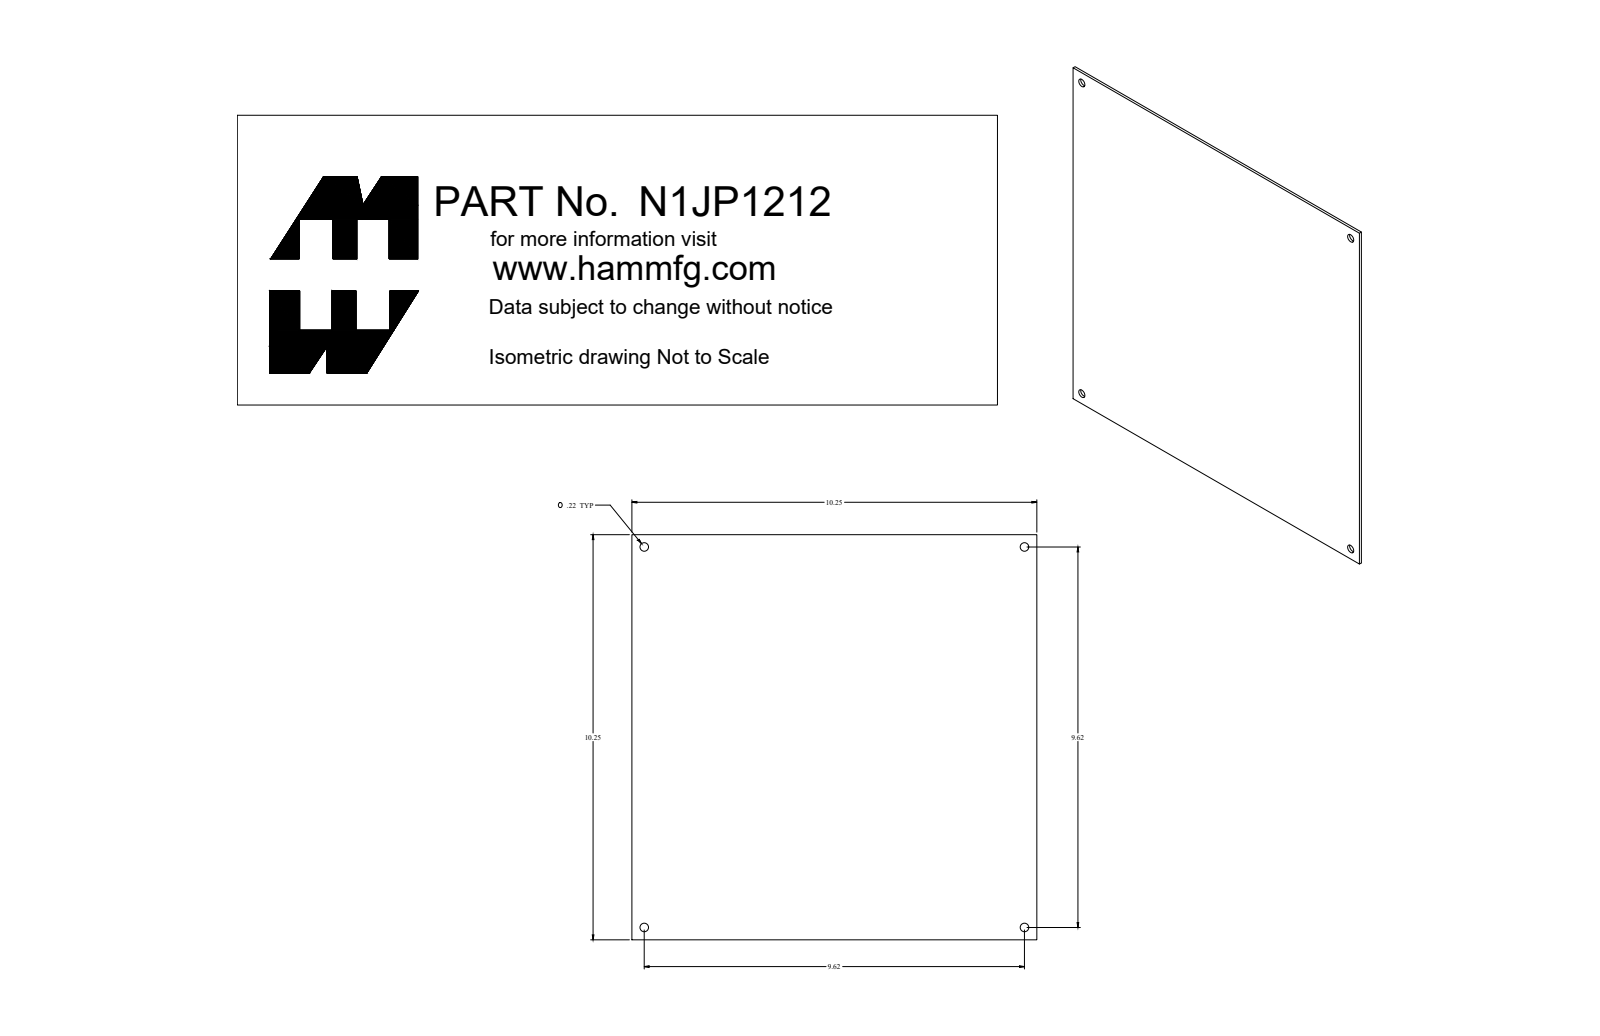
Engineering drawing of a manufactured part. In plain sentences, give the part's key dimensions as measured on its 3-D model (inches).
The part is named "N1JP1212". Its 3-D file was written by "SolidWorks 2018 (AUTOMOTIVE_DESIGN)". It is 1 solid with 18 faces: 6 planar, 12 cylindrical and 0 other. Overall it measures 10.25 by 10.25 by 0.072 inches. Its volume is 7.548 cubic inches and its surface area 212.8 square inches. Round holes: 2 of diameter 0.265, 2 of diameter 0.265. Partial cylindrical surfaces (rounded edges, fillets, slot ends): 4 of radius 0.125. The main face-to-face distances are 0.072, 10.25. The hole center spacings are 9.625, 13.611.
